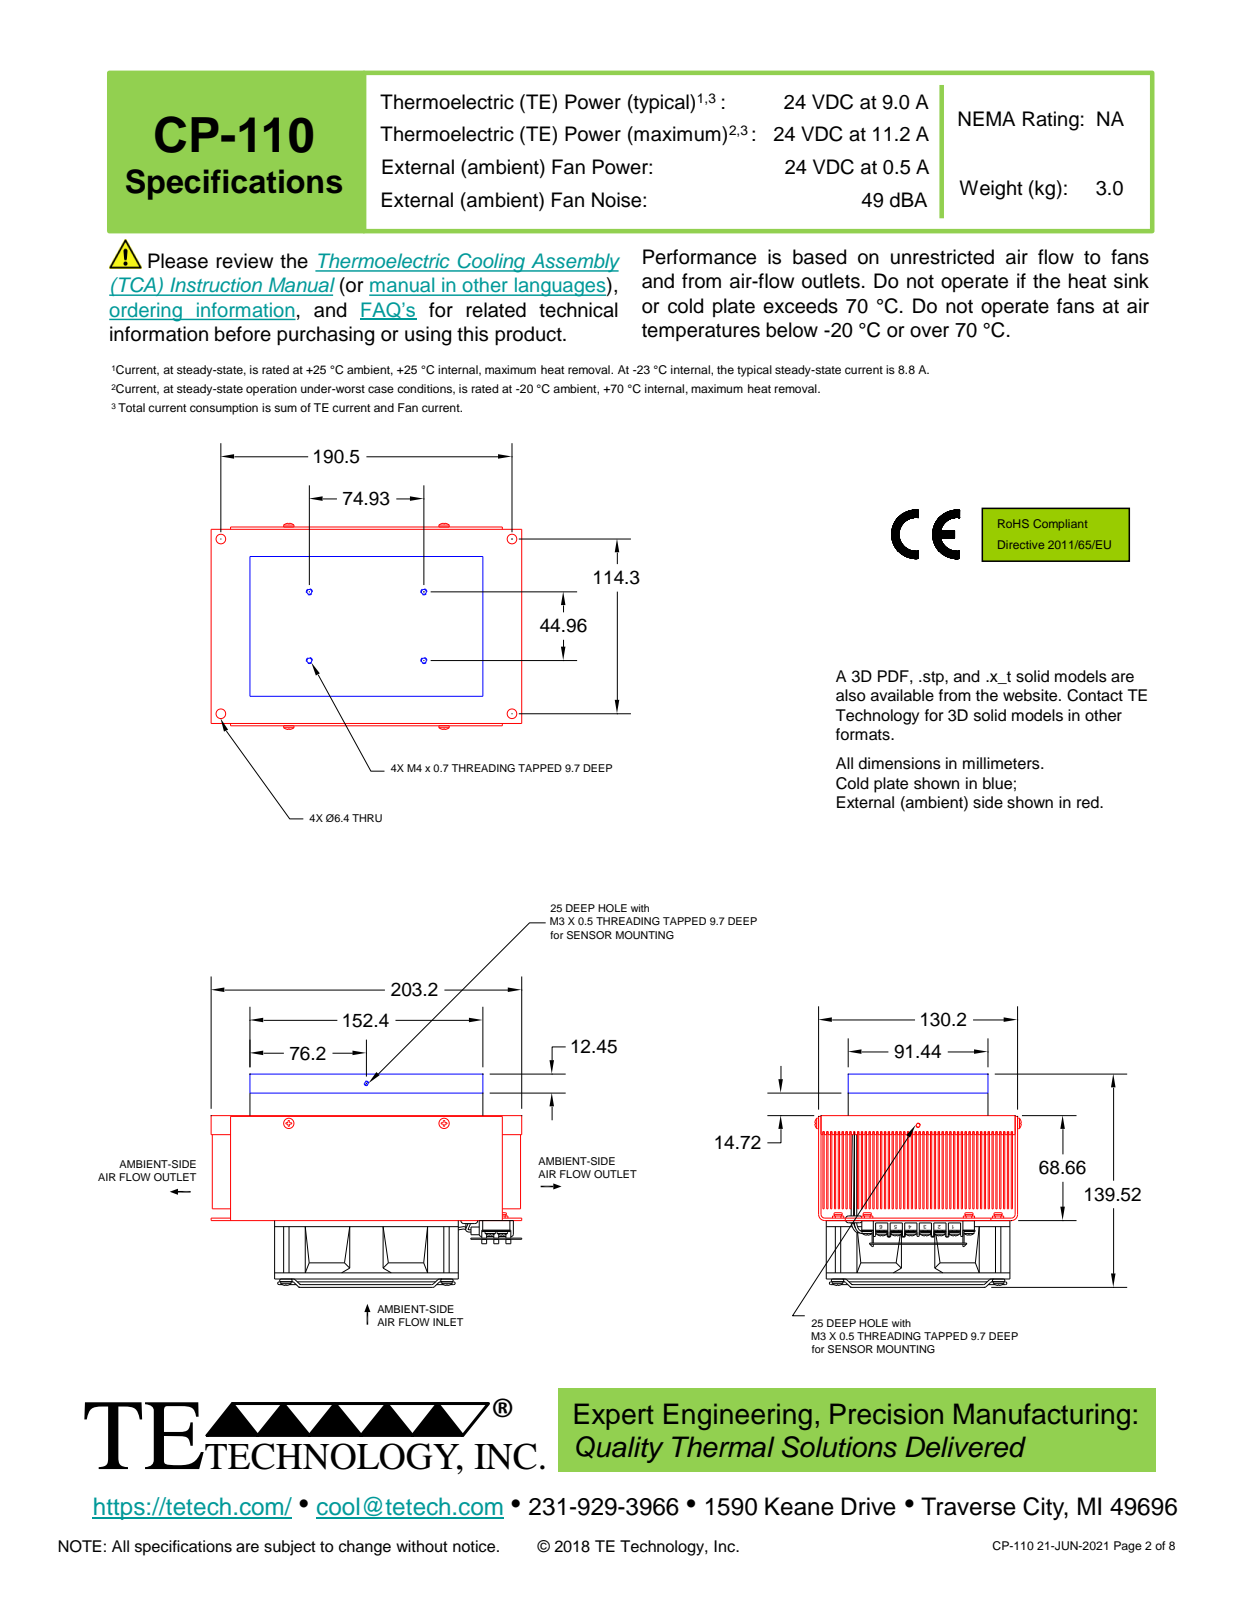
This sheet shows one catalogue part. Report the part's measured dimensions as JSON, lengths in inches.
{"part_name": "4658 heat sink assy; 3111 G heat sink shroud; PEM LKS 6-32-2; 3111-G shroud with PEMS (+8 more)", "step_written_by": "Alibre (AUTOMOTIVE_DESIGN)", "units": "inches", "bodies": {"solids": 118, "faces": 2957, "planar": 1754, "cylindrical": 608, "other": 595}, "overall_size": [8.006, 5.493, 5.318], "volume_in3": 79.31, "surface_area_in2": 1925, "round_holes": [[0.104, 18], [0.104, 8], [0.166, 8], [0.219, 8], [0.25, 8], [0.17, 6], [0.19, 5], [0.075, 4], [0.128, 4], [0.139, 4], [0.155, 4], [0.164, 4]], "round_bosses_or_shafts": [[0.138, 26], [0.27, 18], [0.065, 10], [0.056, 10], [0.071, 9], [0.25, 8], [0.406, 4], [0.375, 4]], "partial_cylinders_radius": [[0.039, 44], [0.02, 29], [0.038, 21], [0.031, 16], [0.079, 12], [0.015, 8], [0.03, 8], [0.031, 8]], "face_to_face_distances": [0.396, 0.198, 0.099, 0.495, 0.297, 0.594, 0.891, 0.297, 0.693, 0.792], "hole_center_spacings": [0.31, 0.75, 0.811, 0.375, 0.375, 0.486, 0.487, 0.747]}
